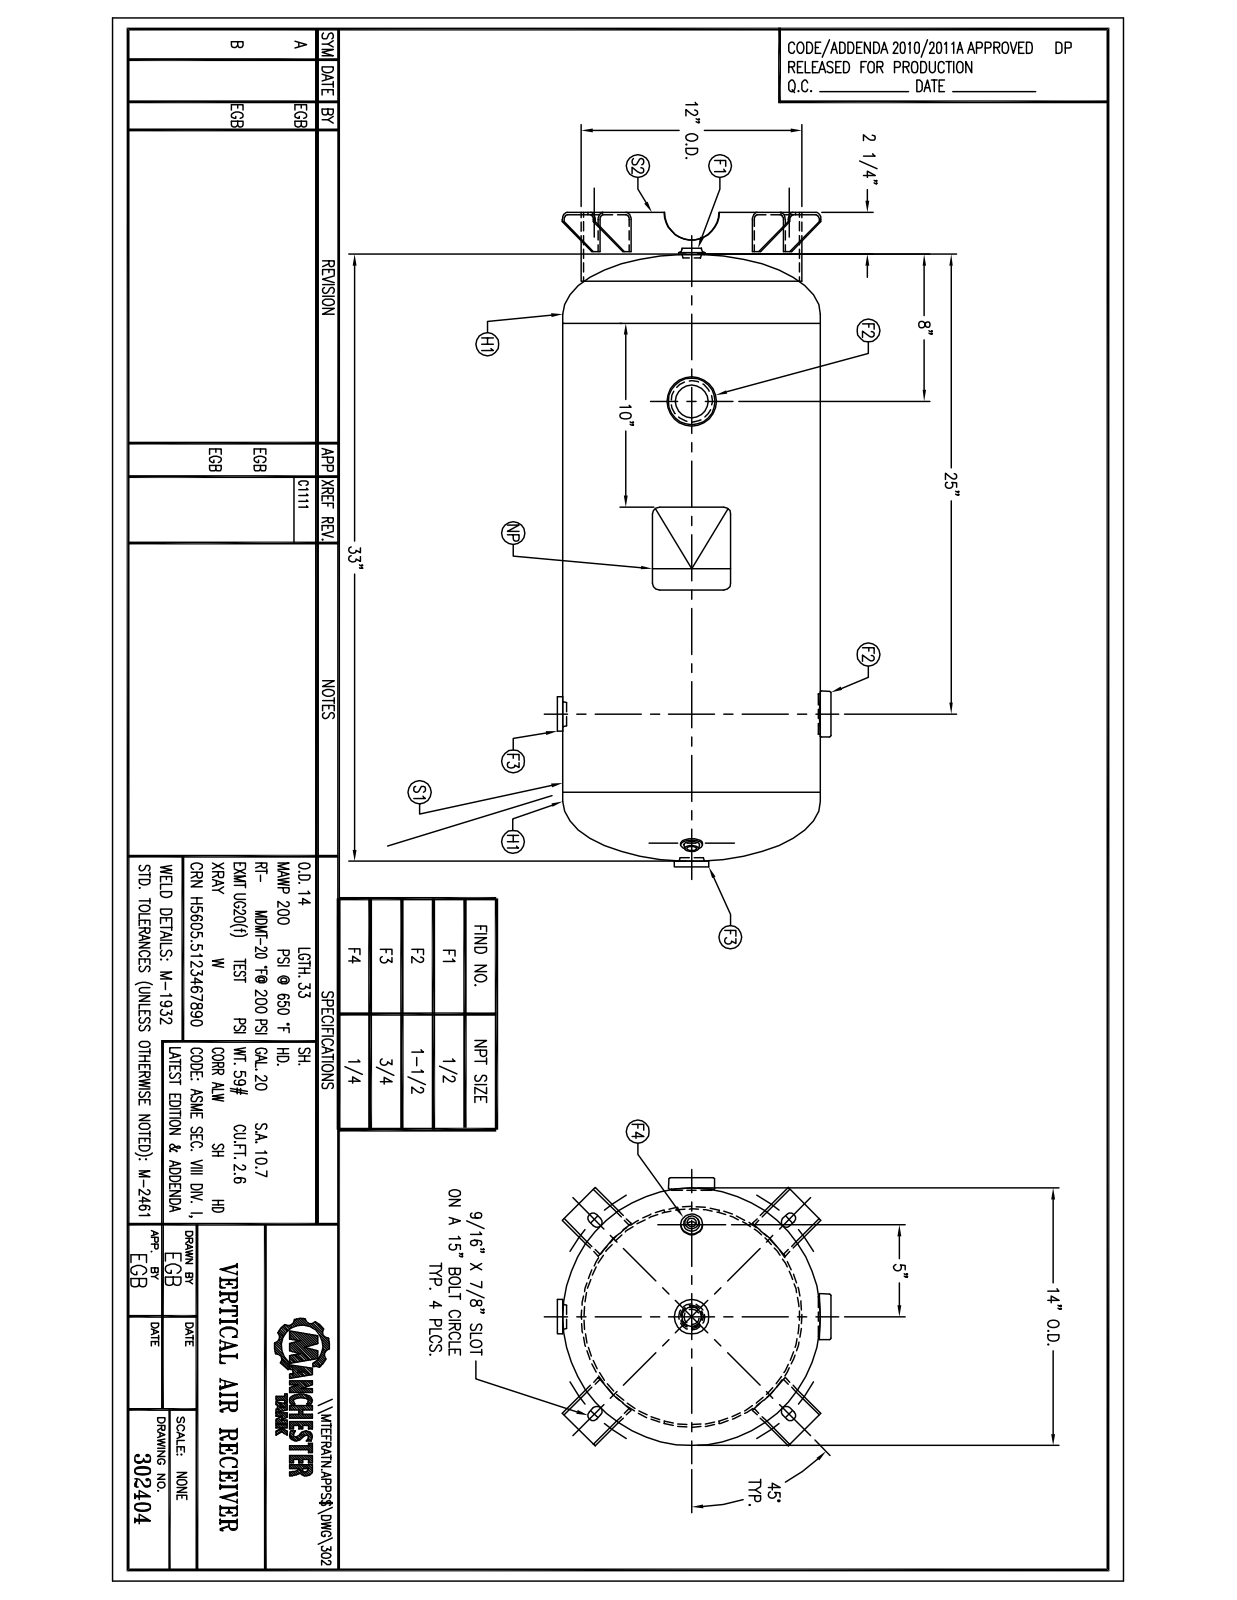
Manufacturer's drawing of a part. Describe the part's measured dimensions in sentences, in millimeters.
The part is named "302404". Its 3-D file was written by "SolidWorks 2011 (CONFIG_CONTROL_DESIGN)". It is 0 solids with 257 faces: 104 planar, 75 cylindrical and 78 other. Overall it measures 903.8 by 378.6 by 372.9 millimeters. Round holes: 2 of diameter 26.7, 2 of diameter 48.3, 1 of diameter 13.7, 1 of diameter 21.3, 1 of diameter 298, 1 of diameter 350.2. Round bosses or shafts: 2 of diameter 68.3, 2 of diameter 41.4, 2 of diameter 36.8, 2 of diameter 36.5, 1 of diameter 355.6, 1 of diameter 350.5, 1 of diameter 304.8, 1 of diameter 57.6. Partial cylindrical surfaces (rounded edges, fillets, slot ends): 8 of radius 6.4, 8 of radius 7.1, 8 of radius 9.8, 1 of radius 179.3. The main face-to-face distances are 3.4, 60.5, 63.9, 57.2, 91.8, 95.3, 58.4, 150.3, 153.7, 647.7.
